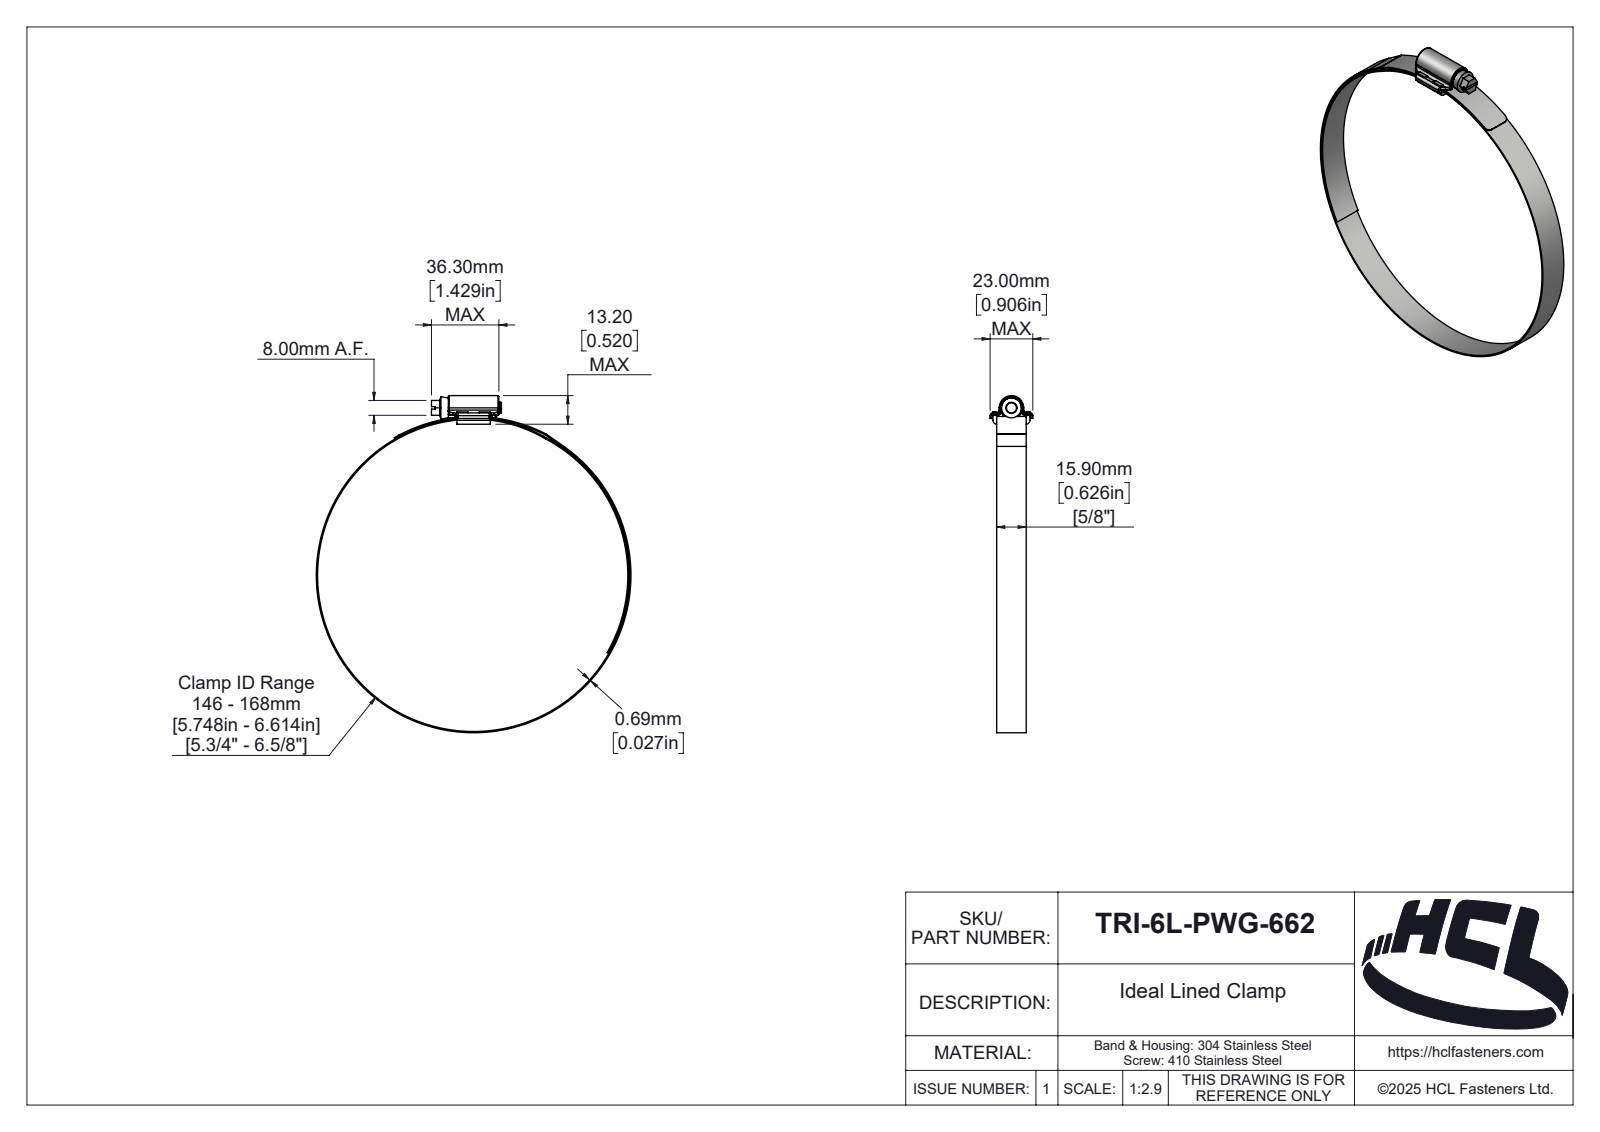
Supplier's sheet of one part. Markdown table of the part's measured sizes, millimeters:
| quantity | value |
| --- | --- |
| part name | TRI-6L-PWG-662 |
| STEP written by | SolidWorks 2025 (AUTOMOTIVE_DESIGN) |
| units | millimeters |
| bodies | 4 solids, 268 faces (87 planar, 102 cylindrical, 79 other) |
| overall size | 181.39 × 169.38 × 23 |
| volume | 13 418 mm³ |
| surface area | 29 481 mm² |
| round holes (diameter × count) | 168 × 1 |
| round bosses / shafts (diameter × count) | 169.38 × 1, 10.7 × 1, 6 × 1 |
| partial cylindrical surfaces (radius × count) | 1 × 14, 0.5 × 4, 1.5 × 4, 2 × 3, 0.1 × 2, 2.1 × 2, 3 × 2, 0.46 × 1 |
| main face-to-face distances | 15.9, 2, 0.69, 17.9, 4.9, 1.2, 4.55, 3.35, 15.35, 2.55 |
